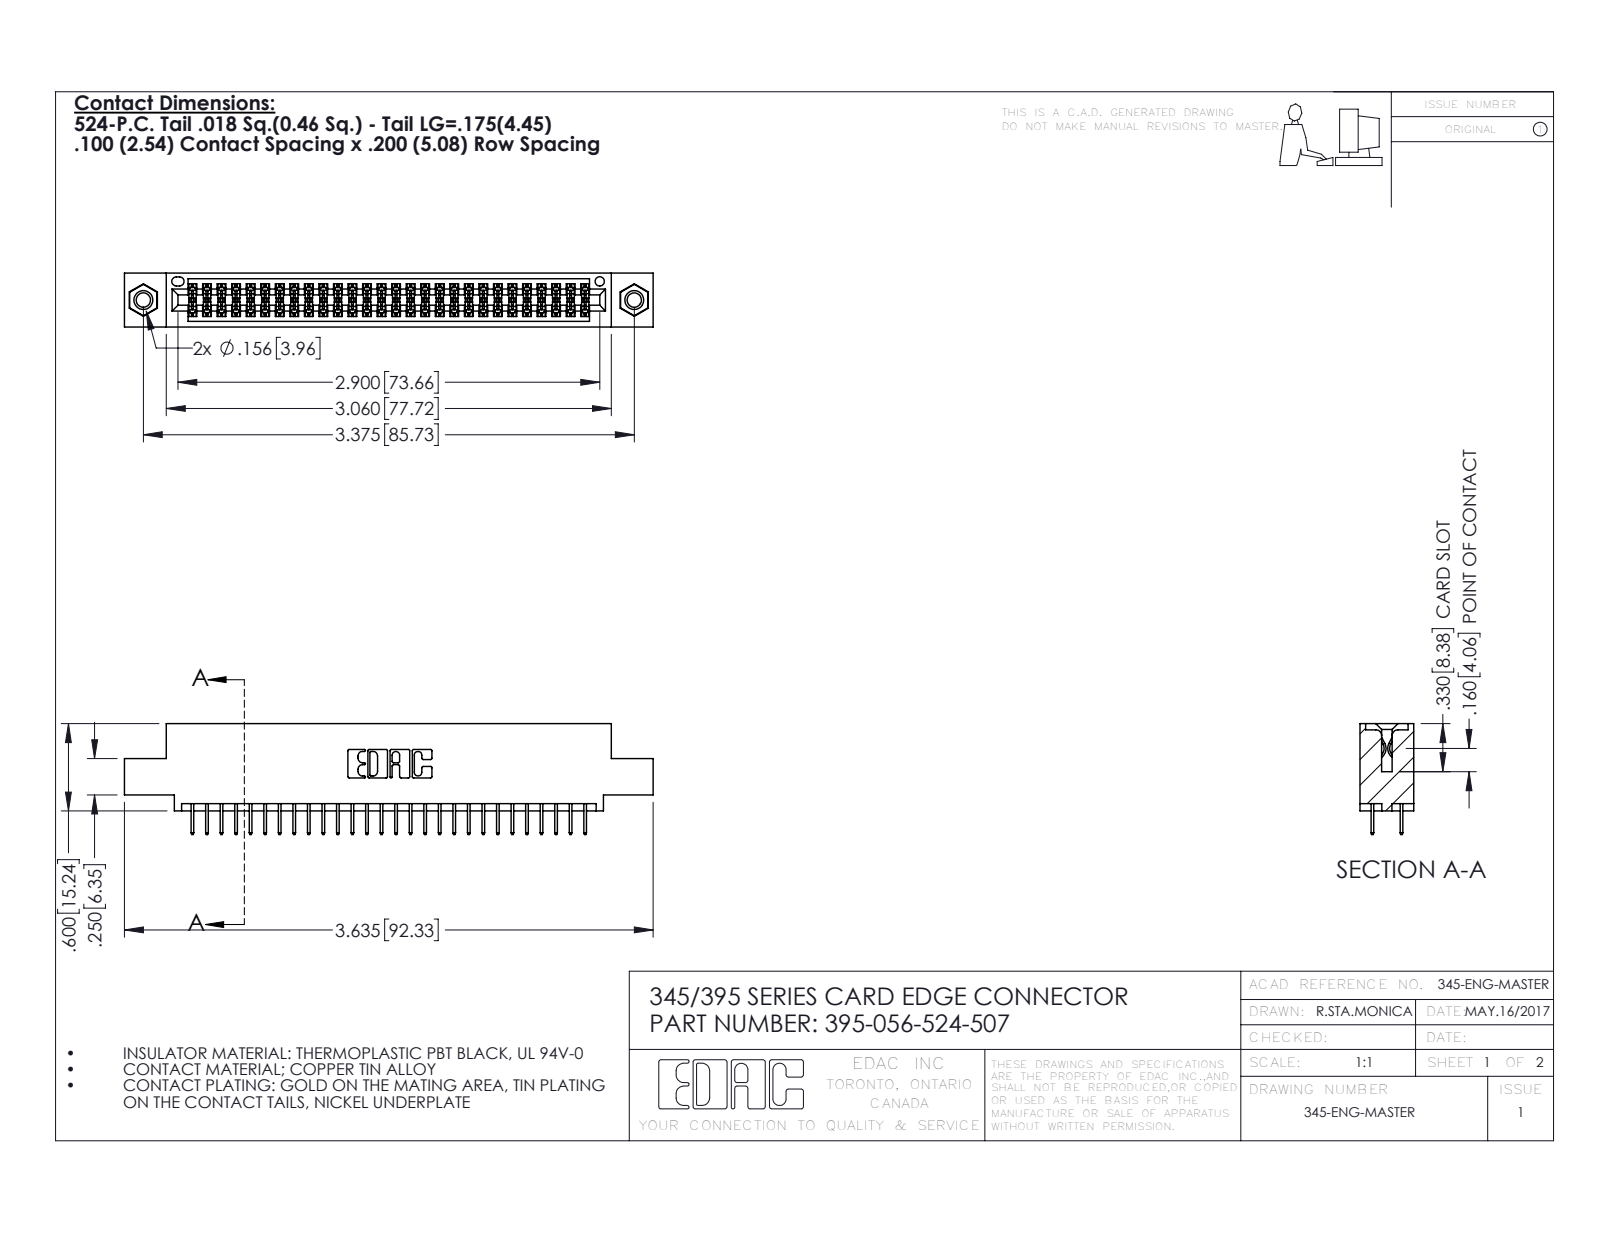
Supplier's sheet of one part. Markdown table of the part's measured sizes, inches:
| quantity | value |
| --- | --- |
| part name | 345-292-001_345-293-124; 395-056-524-507; 345 Part_0.110 Offset - 0.156 Dia-TI; 345-250-001_345-250-005-103 |
| STEP written by | SolidWorks 2016 (CONFIG_CONTROL_DESIGN) |
| units | inches |
| bodies | 59 solids, 3214 faces (2300 planar, 898 cylindrical, 16 other) |
| overall size | 3.635 × 0.762 × 0.37 |
| volume | 0.529 in³ |
| surface area | 19.28 in² |
| round holes (diameter × count) | 0.098 × 2, 0.125 × 2, 0.156 × 2, 0.064 × 1 |
| round bosses / shafts (diameter × count) | 0.155 × 2 |
| partial cylindrical surfaces (radius × count) | 0.006 × 84, 0.01 × 22, 0.007 × 6, 0.031 × 6, 0.026 × 3, 0.014 × 2, 0.019 × 2, 0.022 × 2 |
| main face-to-face distances | 0.072, 0.298, 0.2, 0.37, 0.098, 0.272, 0.025, 0.225, 0.072, 0.175 |
| hole center spacings | 0.27, 3.14, 3.375 |
